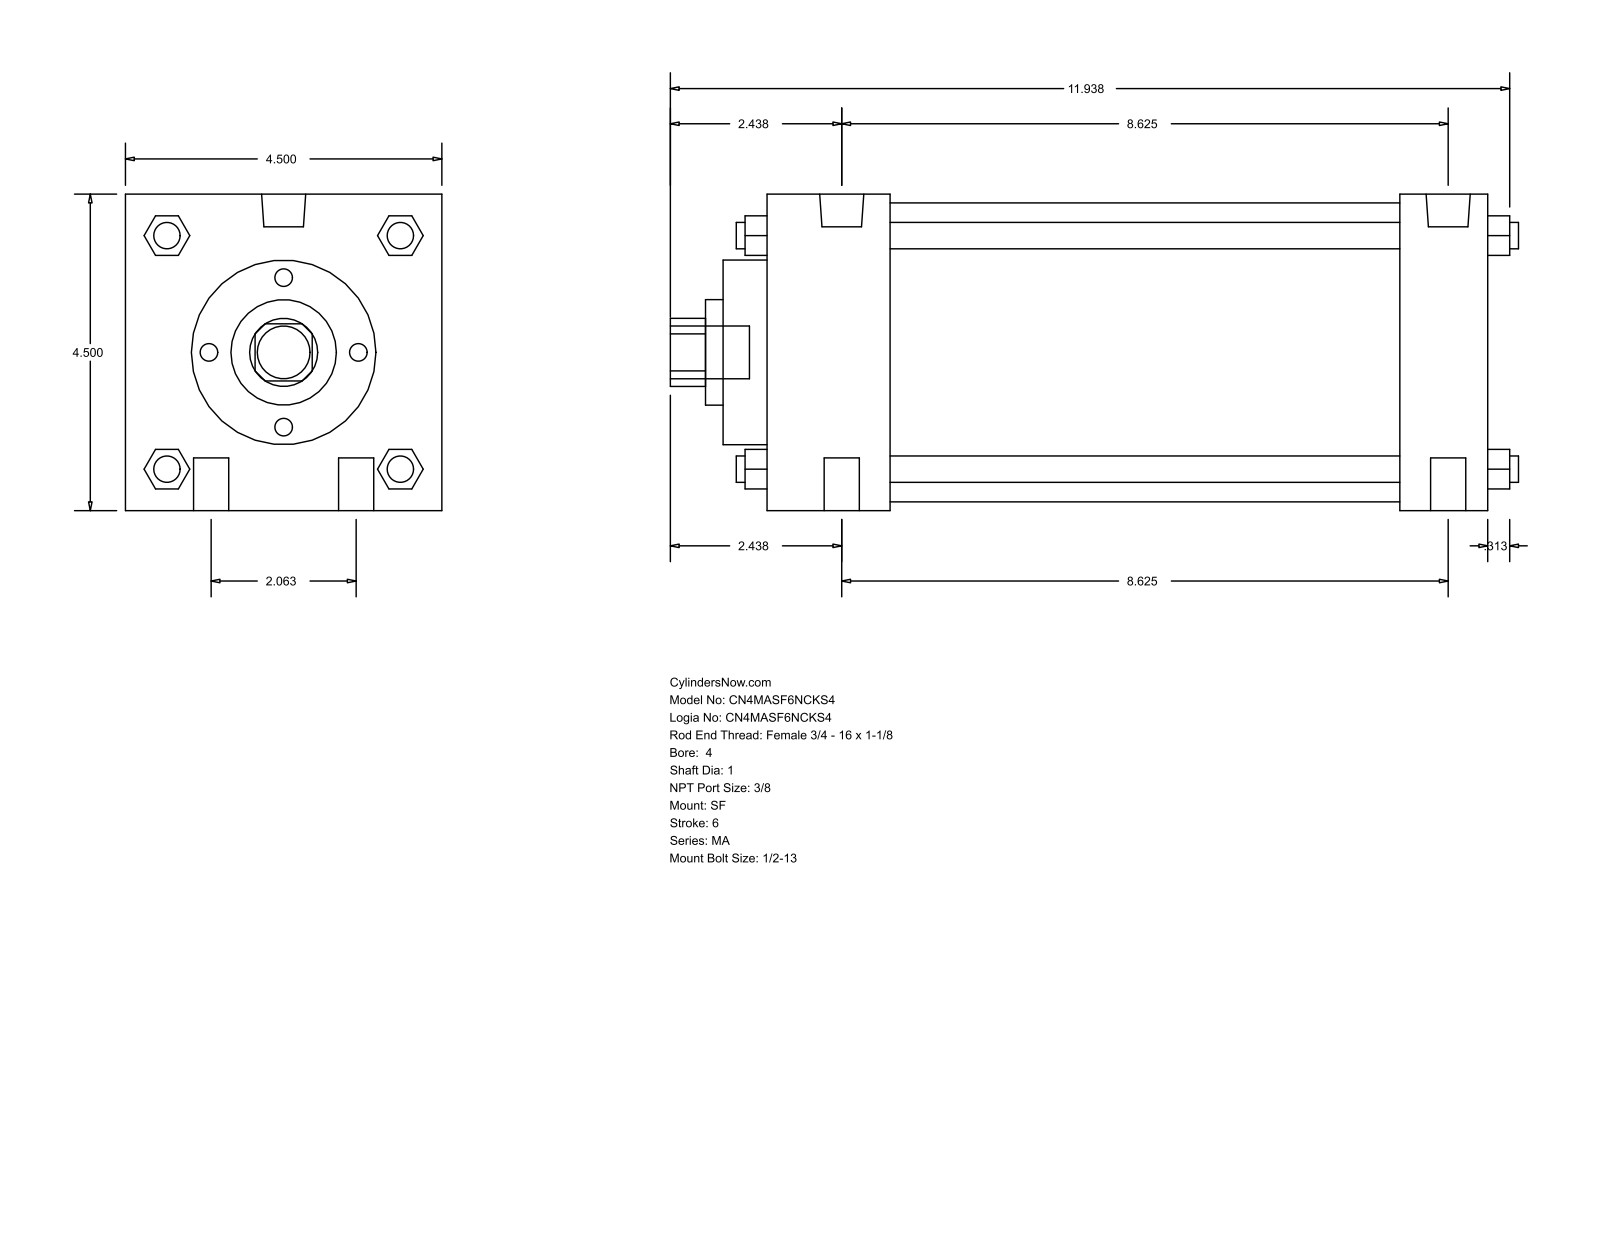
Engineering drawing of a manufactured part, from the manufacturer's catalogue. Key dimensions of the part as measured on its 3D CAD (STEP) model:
Part name (STEP PRODUCT): MA_SF__0400_1
STEP written by: GSSL Pune (CONFIG_CONTROL_DESIGN)
Units: millimetres
Bodies: 0 solids, 126 faces (95 planar, 31 cylindrical, 0 other)
Overall size (bounding box): 306.39 × 114.3 × 114.3
Round holes (diameter × count): ⌀25.4 ×1, ⌀38.1 ×1, ⌀66.67 ×1, ⌀107.95 ×1
Round bosses / shafts (diameter × count): ⌀12.7 ×4, ⌀9.53 ×4, ⌀15.93 ×2, ⌀11.11 ×2, ⌀19.05 ×1
Partial cylindrical surfaces — rounded edges, fillets, slot ends (radius × count): R12.29 ×1
Main face-to-face distances: 114.3, 260.35, 228.6, 31.75, 44.46, 184.14, 215.89, 276.22, 15.87, 60.33
